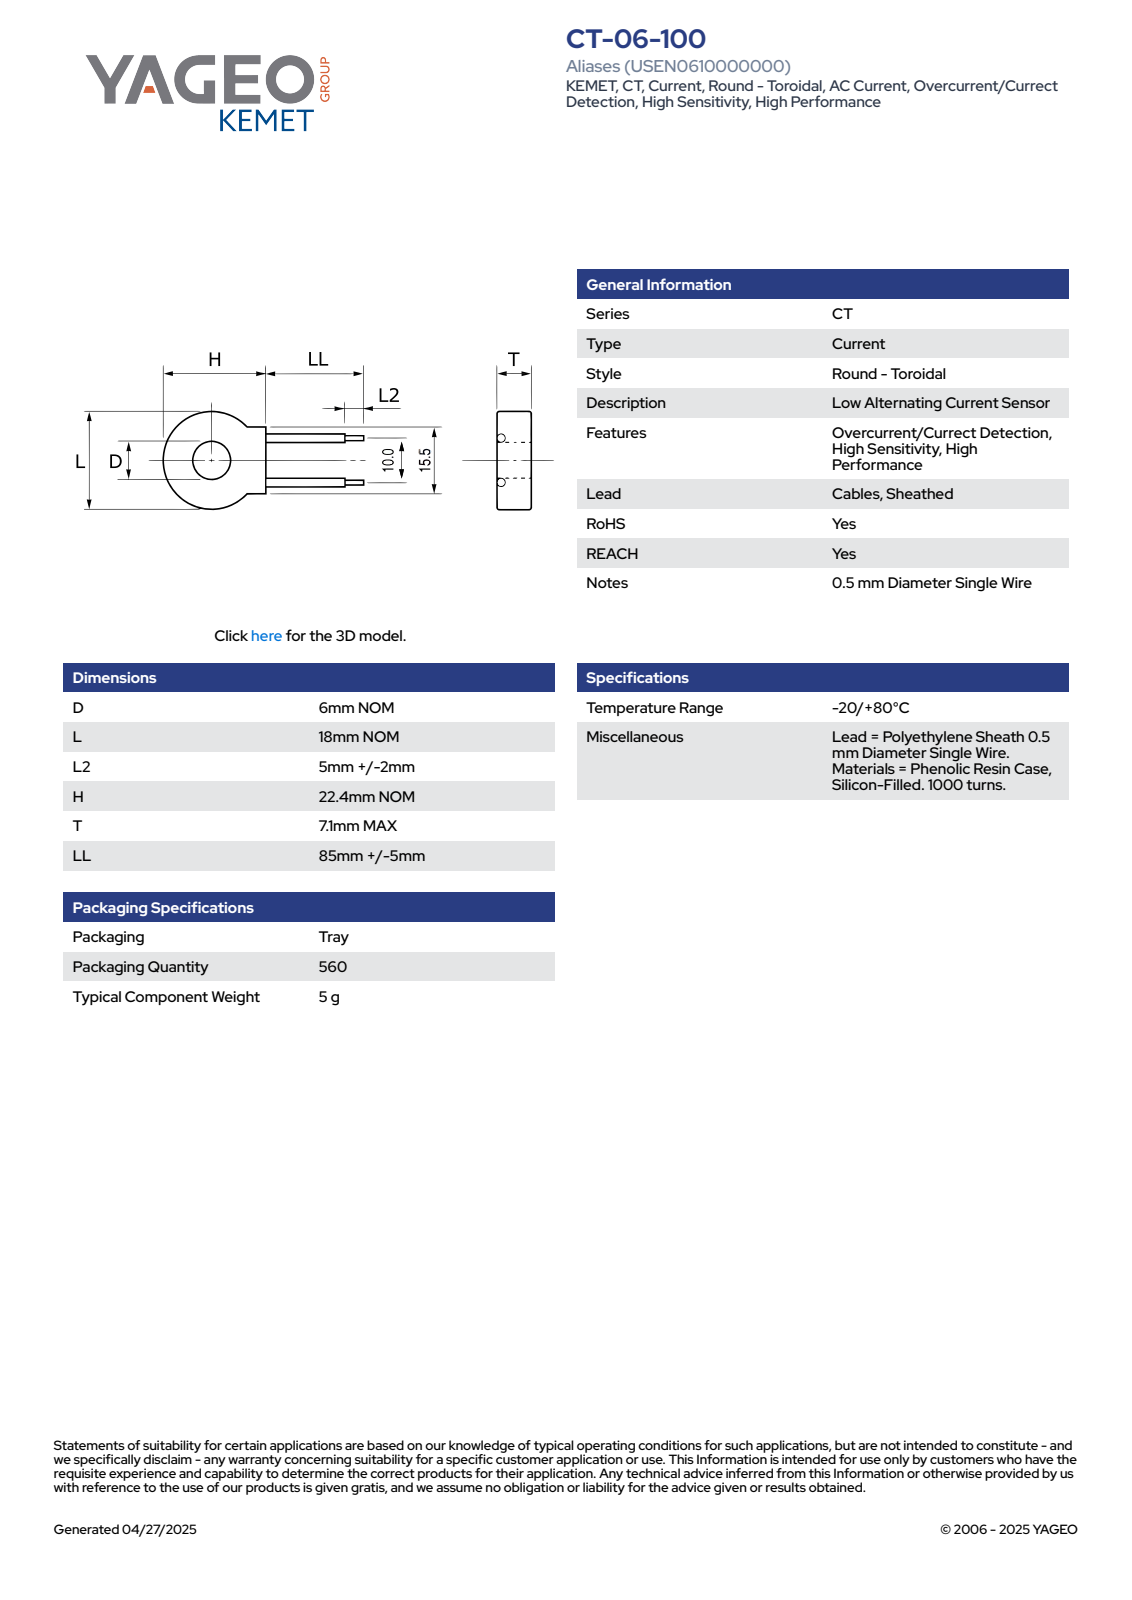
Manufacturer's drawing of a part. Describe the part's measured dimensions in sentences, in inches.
The part is named "SC_CT06_D6L18L27H22.4T7.1LL90". Its 3-D file was written by "SolidWorks 2014 (AUTOMOTIVE_DESIGN)". It is 1 solid with 78 faces: 31 planar, 16 cylindrical and 31 other. Overall it measures 4.425 by 0.709 by 0.28 inches. Its volume is 0.155 cubic inches and its surface area 3.246 square inches. Round holes: 1 of diameter 0.236. Round bosses or shafts: 2 of diameter 0.059, 2 of diameter 0.039. Partial cylindrical surfaces (rounded edges, fillets, slot ends): 1 of radius 0.354, 1 of radius 0.354. The main face-to-face distances are 0.28, 0.61, 3.268, 3.543, 0.276, 0.1, 0.18, 0.08, 0.115, 0.164.
